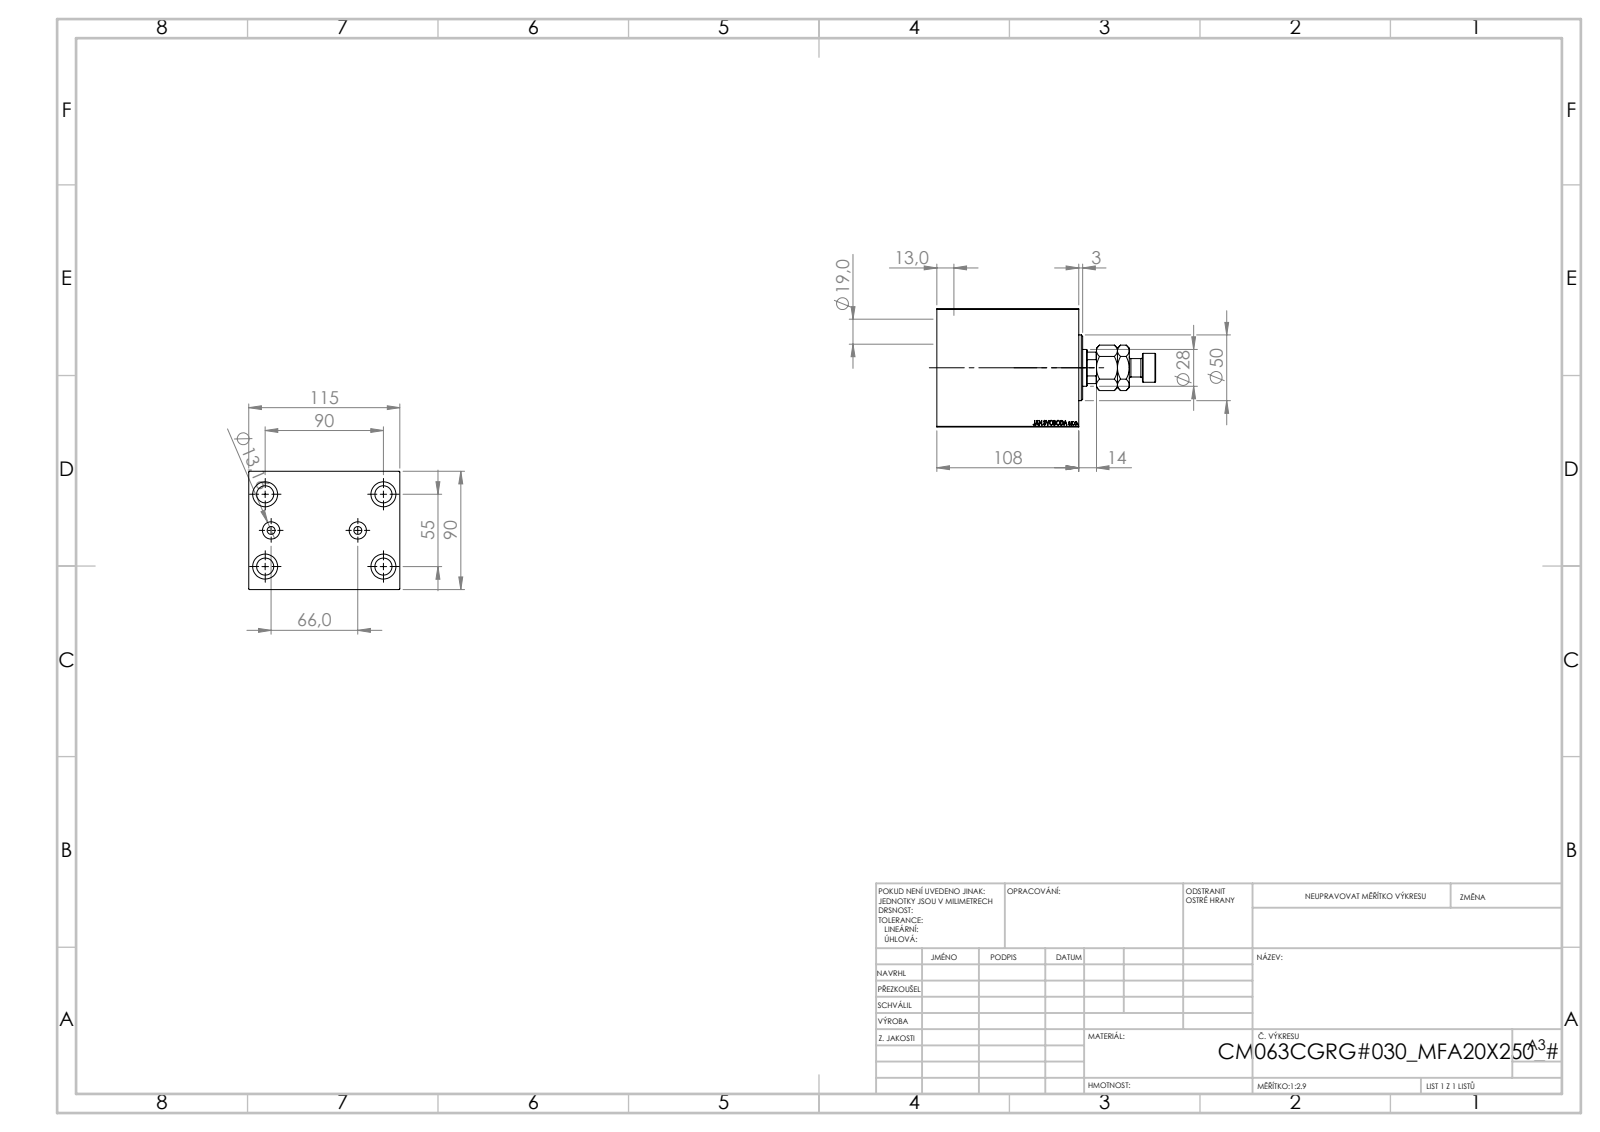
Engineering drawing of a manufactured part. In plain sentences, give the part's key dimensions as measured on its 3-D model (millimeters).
The part is named "V450CM_C_Body; MFA; V450CM_C_VCP; V450CM_VC_B". Its 3-D file was written by "SolidWorks 2019 (CONFIG_CONTROL_DESIGN)". It is 4 solids with 913 faces: 425 planar, 62 cylindrical and 426 other. Overall it measures 166.5 by 115 by 90 millimeters. Its volume is 991 511 cubic millimeters and its surface area 145 299 square millimeters. Round holes: 4 of diameter 13, 4 of diameter 19, 2 of diameter 6, 2 of diameter 13.16, 1 of diameter 18.5, 1 of diameter 28, 1 of diameter 31.5, 1 of diameter 63, 1 of diameter 65, 1 of diameter 72. Round bosses or shafts: 1 of diameter 50, 1 of diameter 22, 1 of diameter 14. Partial cylindrical surfaces (rounded edges, fillets, slot ends): 1 of radius 13.5. The main face-to-face distances are 90, 115, 108, 89, 19, 30, 29.3, 59.7, 78.7, 59.3. The hole center spacings are 30, 52.74, 82.71, 33, 55, 90, 105.48, 66.
